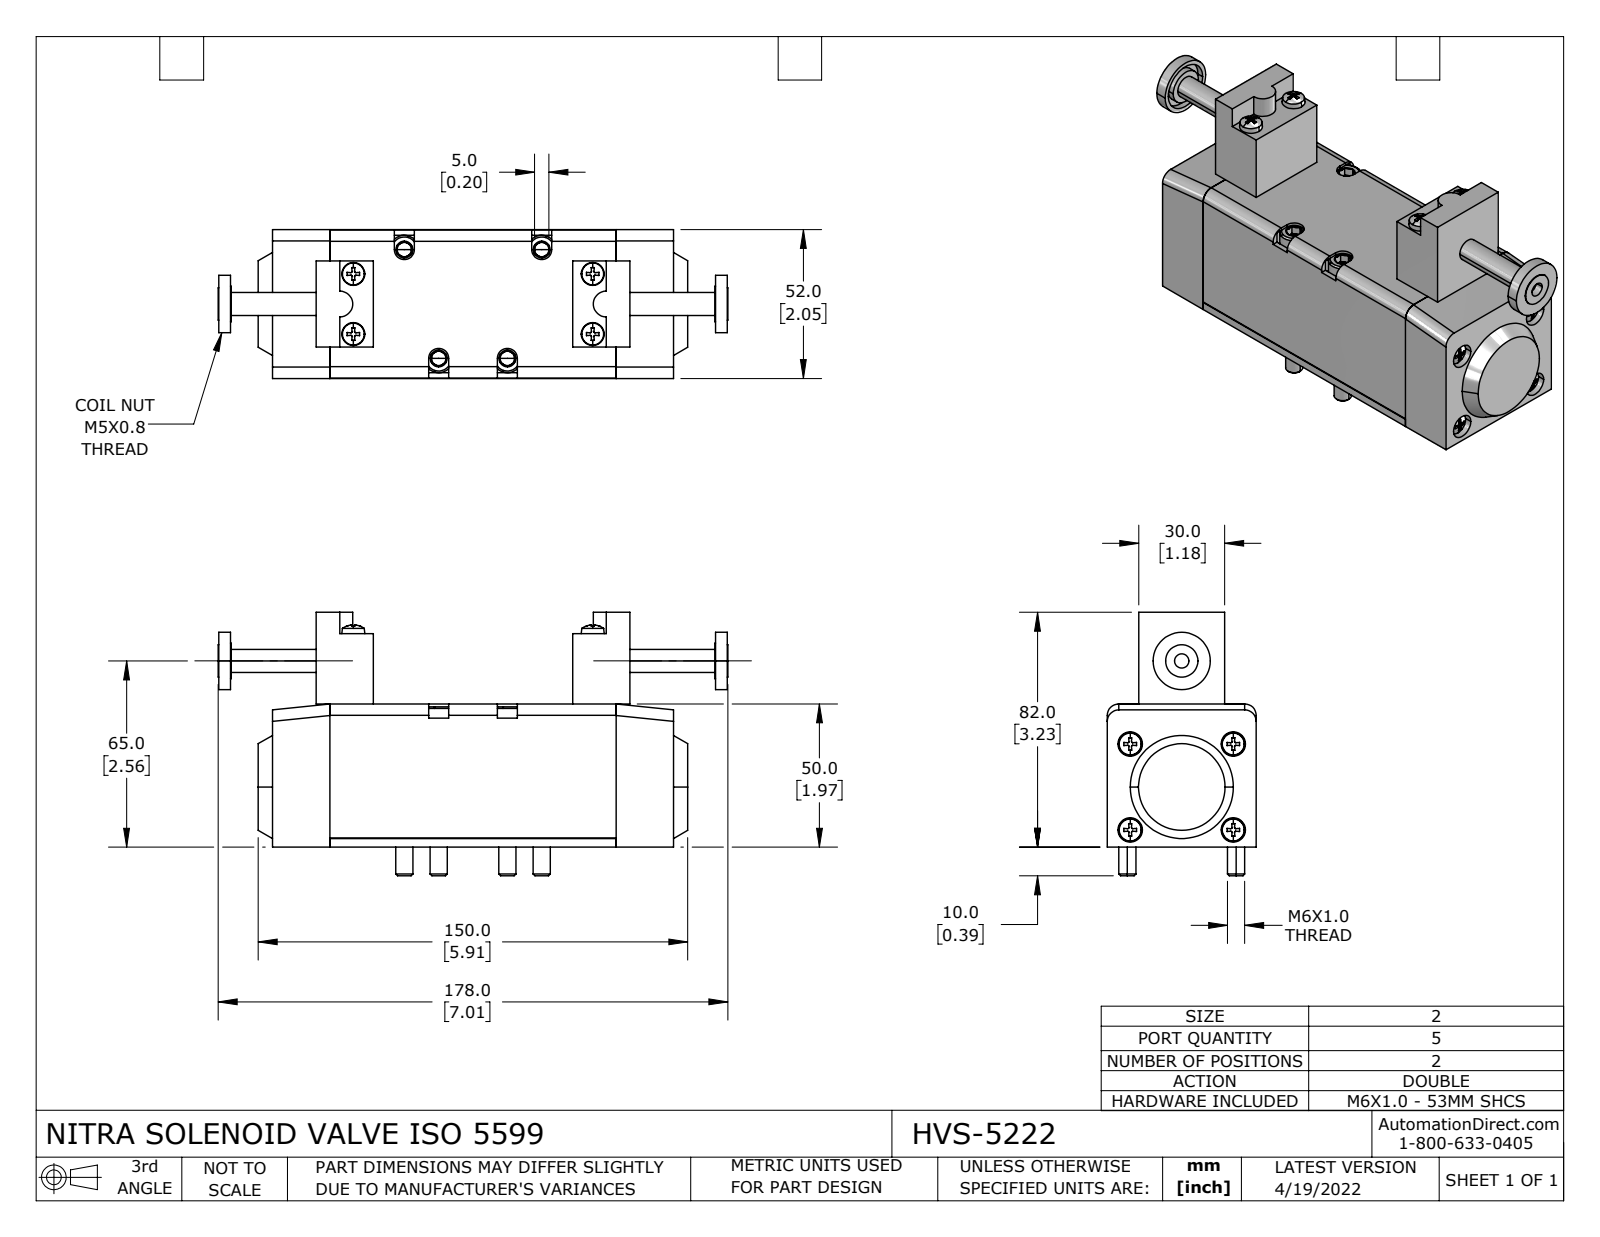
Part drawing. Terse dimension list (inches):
name: HVS-5222
written by: SolidWorks 2021 (CONFIG_CONTROL_DESIGN)
unit: in
bodies: 21 solids, 850 faces (434 planar, 156 cylindrical, 260 other)
size: 7.008 × 3.622 × 2.047
volume: 24.75 in³; area: 119.3 in²
holes: 8× ⌀0.128, 4× ⌀0.161, 4× ⌀0.256, 4× ⌀0.335, 1× ⌀0.197, 1× ⌀0.665
bosses: 8× ⌀0.157, 4× ⌀0.394, 4× ⌀0.236, 1× ⌀0.787, 1× ⌀0.488, 1× ⌀0.445, 1× ⌀0.315
rounds: 6× R0.157, 4× R0.138, 4× R0.197, 2× R0.177
face distances: 1.969, 3.937, 2.039, 2.043, 0.787, 0.598, 4.126, 4.724, 0.433, 1.614
hole spacings: 0.777, 0.827, 1.181, 1.22, 1.344, 1.356, 1.417, 1.569
